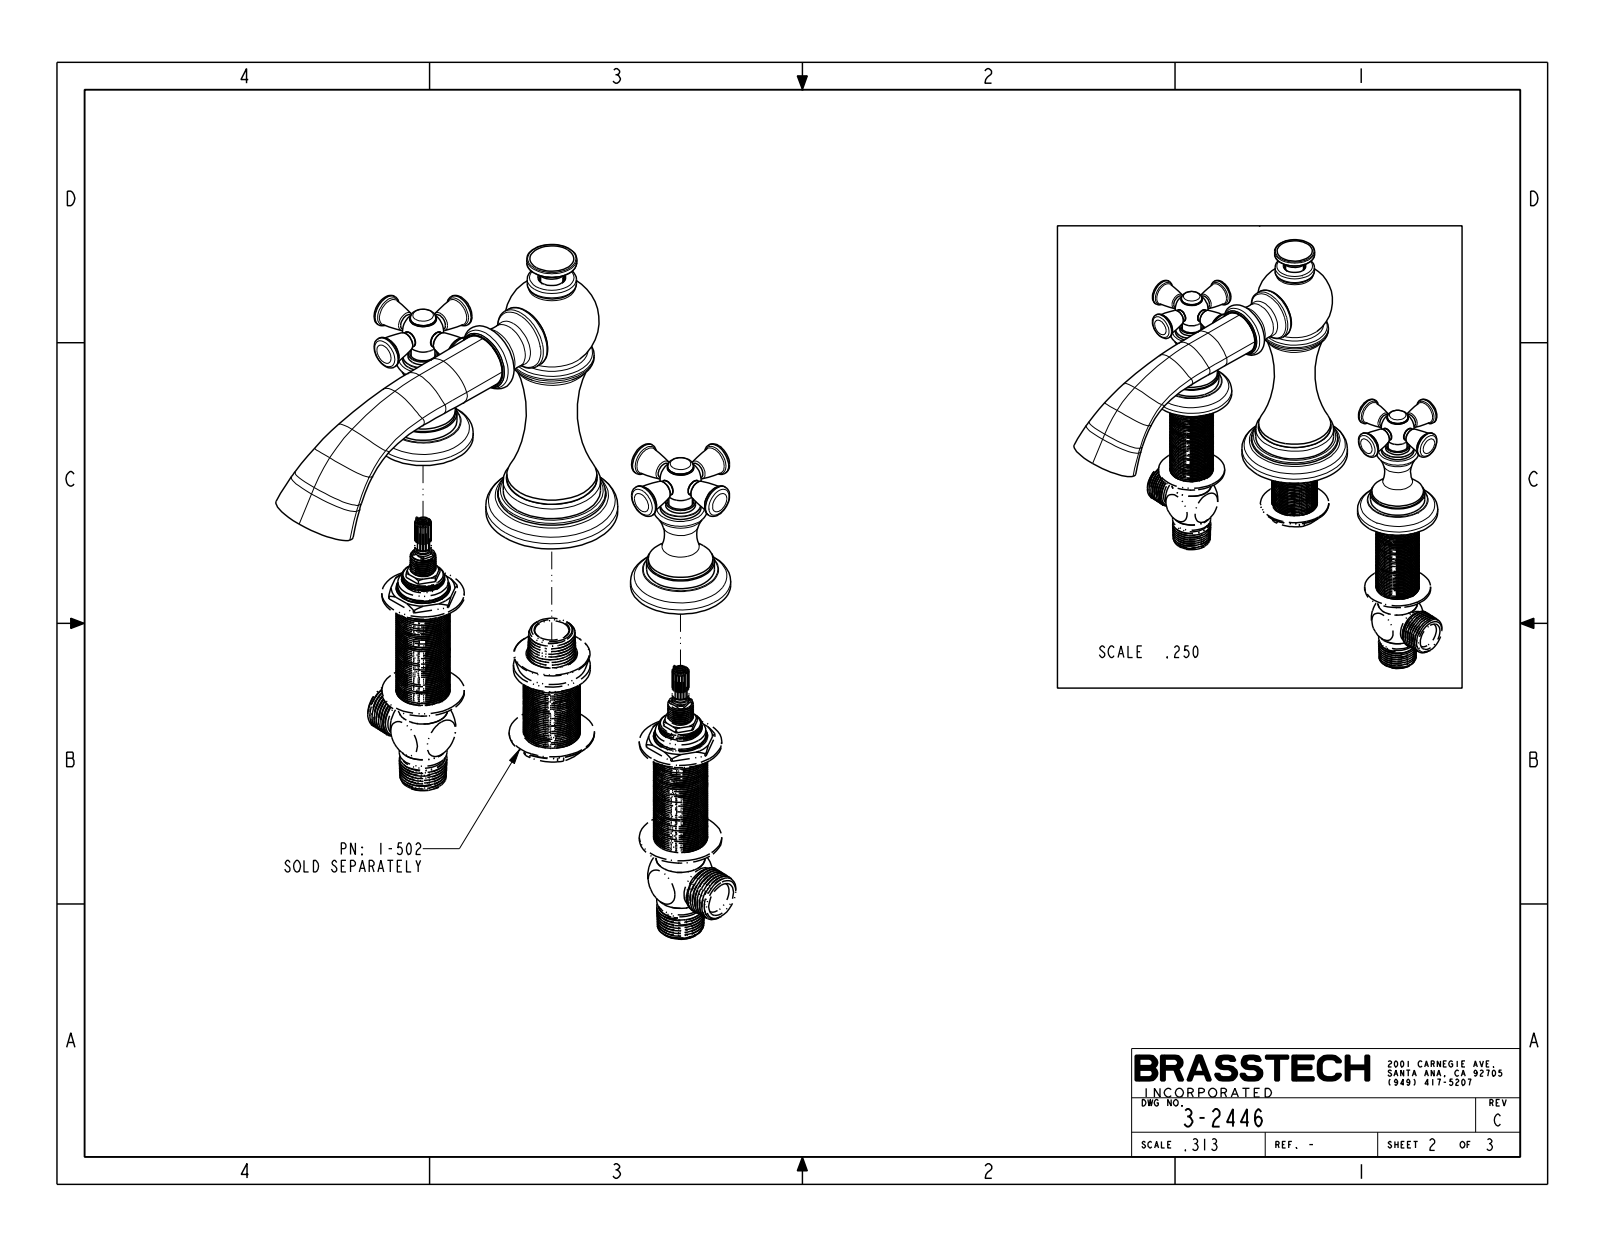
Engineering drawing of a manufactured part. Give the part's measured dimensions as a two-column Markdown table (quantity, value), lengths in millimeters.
| quantity | value |
| --- | --- |
| part name | 3-2446 |
| STEP written by | CREO PARAMETRIC BY PTC INC, 2018400 (CONFIG_CONTROL_DESIGN) |
| units | millimeters |
| bodies | 3 solids, 387 faces (29 planar, 80 cylindrical, 278 other) |
| overall size | 267.4 × 236.2 × 175.8 |
| volume | 513 900 mm³ |
| surface area | 80 710 mm² |
| round bosses / shafts (diameter × count) | 18.3 × 3, 9.1 × 3, 55.9 × 2, 37.8 × 2, 36.1 × 2, 22.9 × 2, 16.8 × 2, 14.2 × 2 |
| main face-to-face distances | 10.9, 2, 159.8, 148.8, 55.1, 44.2, 104.6, 106.7, 53.1, 42.2 |
